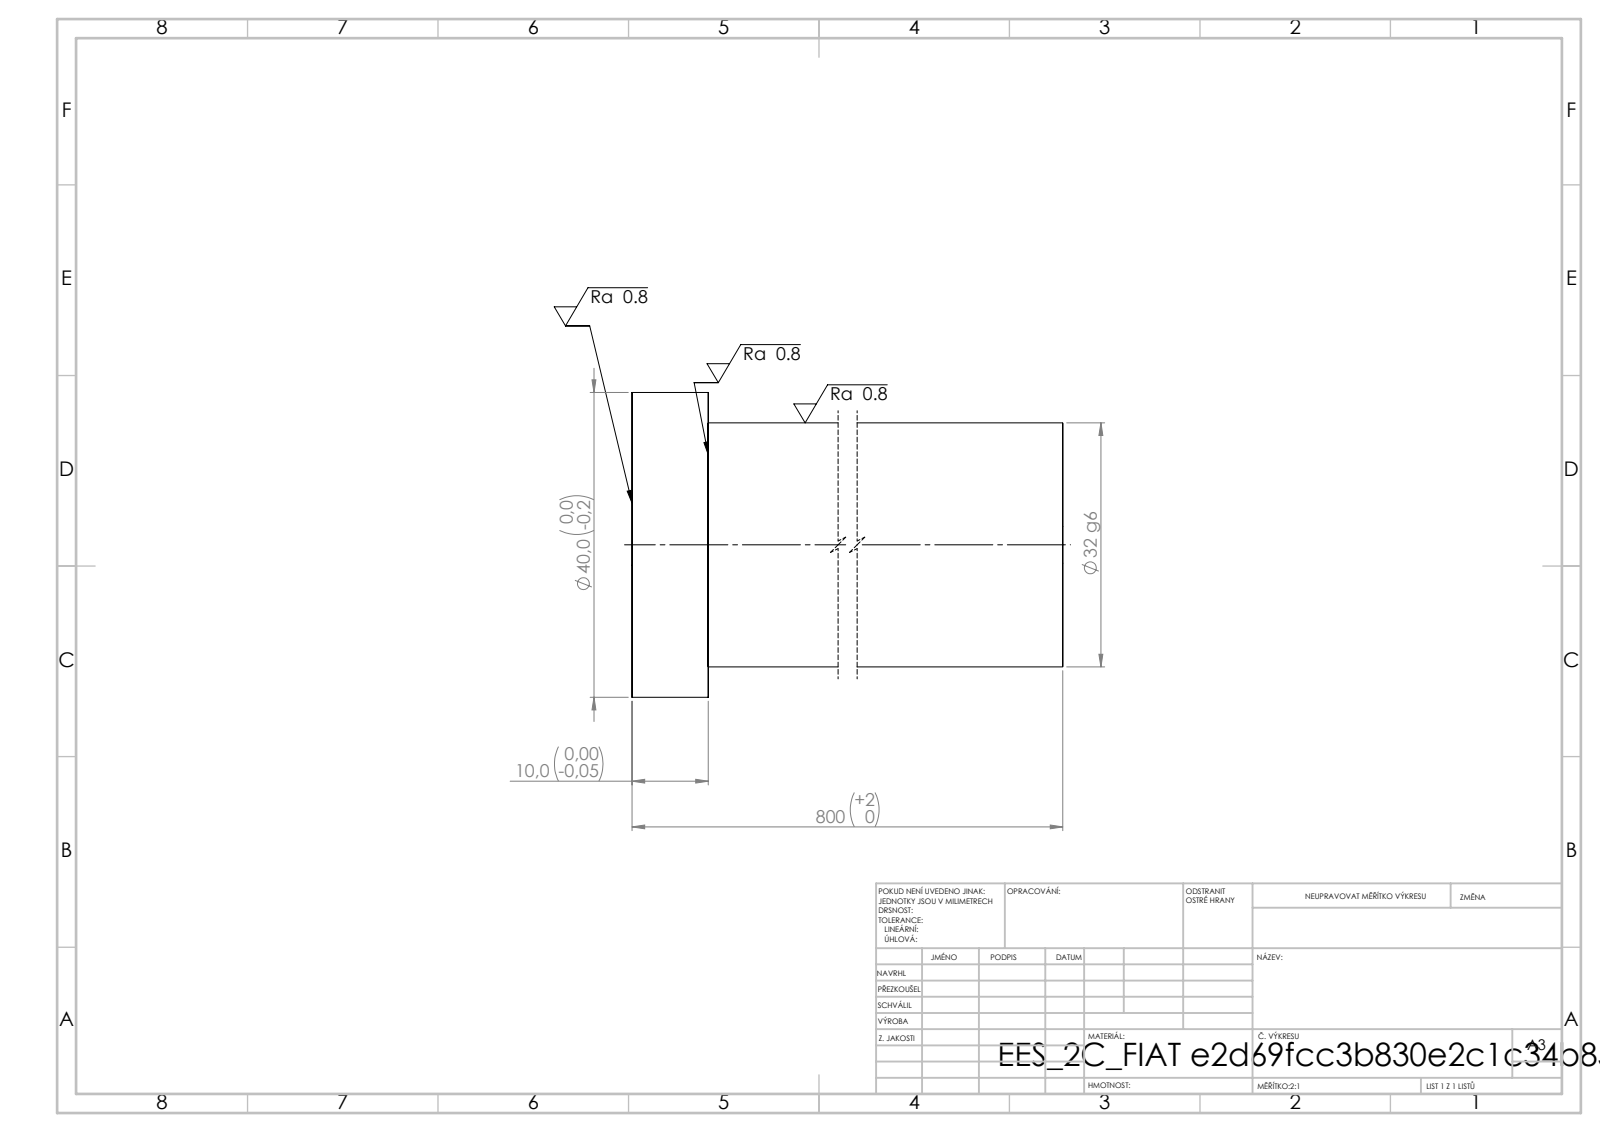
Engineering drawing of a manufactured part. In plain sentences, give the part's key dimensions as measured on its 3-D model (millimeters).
Its 3-D file was written by "SolidWorks 2019 (CONFIG_CONTROL_DESIGN)". It is 1 solid with 7 faces: 3 planar, 4 cylindrical and 0 other. Overall it measures 800 by 40 by 40 millimeters. Its volume is 647 922 cubic millimeters and its surface area 83 189 square millimeters. Round bosses or shafts: 1 of diameter 40, 1 of diameter 32. The main face-to-face distances are 800, 10, 790.
